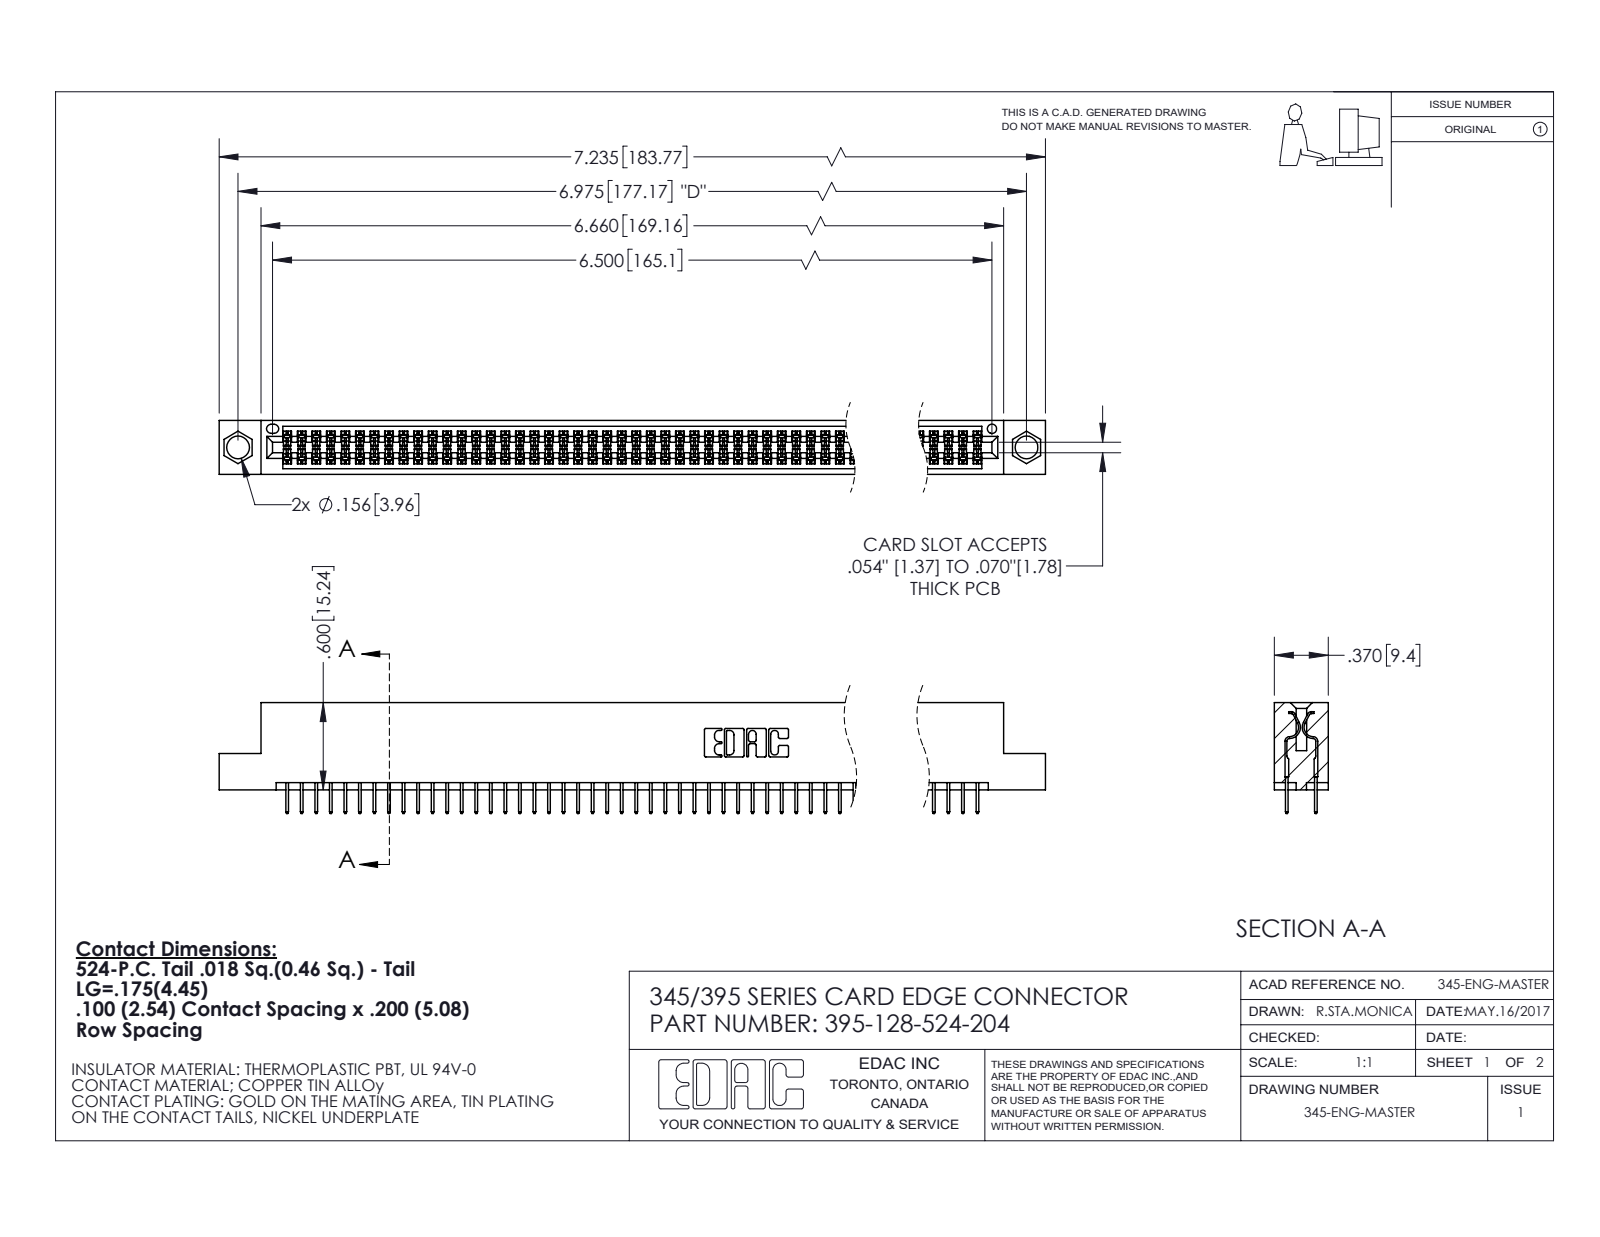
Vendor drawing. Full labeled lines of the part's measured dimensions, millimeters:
Part name (STEP PRODUCT): 395-128-524-204; 345 Part_Flush Mounting Lugs - 0.156 Dia-TI; 345-292-001_345-293-124
STEP written by: SolidWorks 2020 (CONFIG_CONTROL_DESIGN)
Units: millimetres
Bodies: 129 solids, 7052 faces (5086 planar, 1966 cylindrical, 0 other)
Overall size (bounding box): 183.8 × 19.4 × 9.4
Volume: 17 760 mm³ · Surface area: 26 010 mm²
Round holes (diameter × count): ⌀4 ×2, ⌀1.6 ×1
Partial cylindrical surfaces — rounded edges, fillets, slot ends (radius × count): R0.2 ×193, R0.3 ×22, R0.2 ×6, R0.8 ×6, R0.7 ×3, R0.4 ×2, R0.5 ×2, R0.6 ×2
Main face-to-face distances: 1.8, 7.6, 5.1, 9.4, 2.5, 6.9, 0.6, 5.7, 1.8, 4.4
Hole centre spacings: 6.9, 171.2, 177.2
